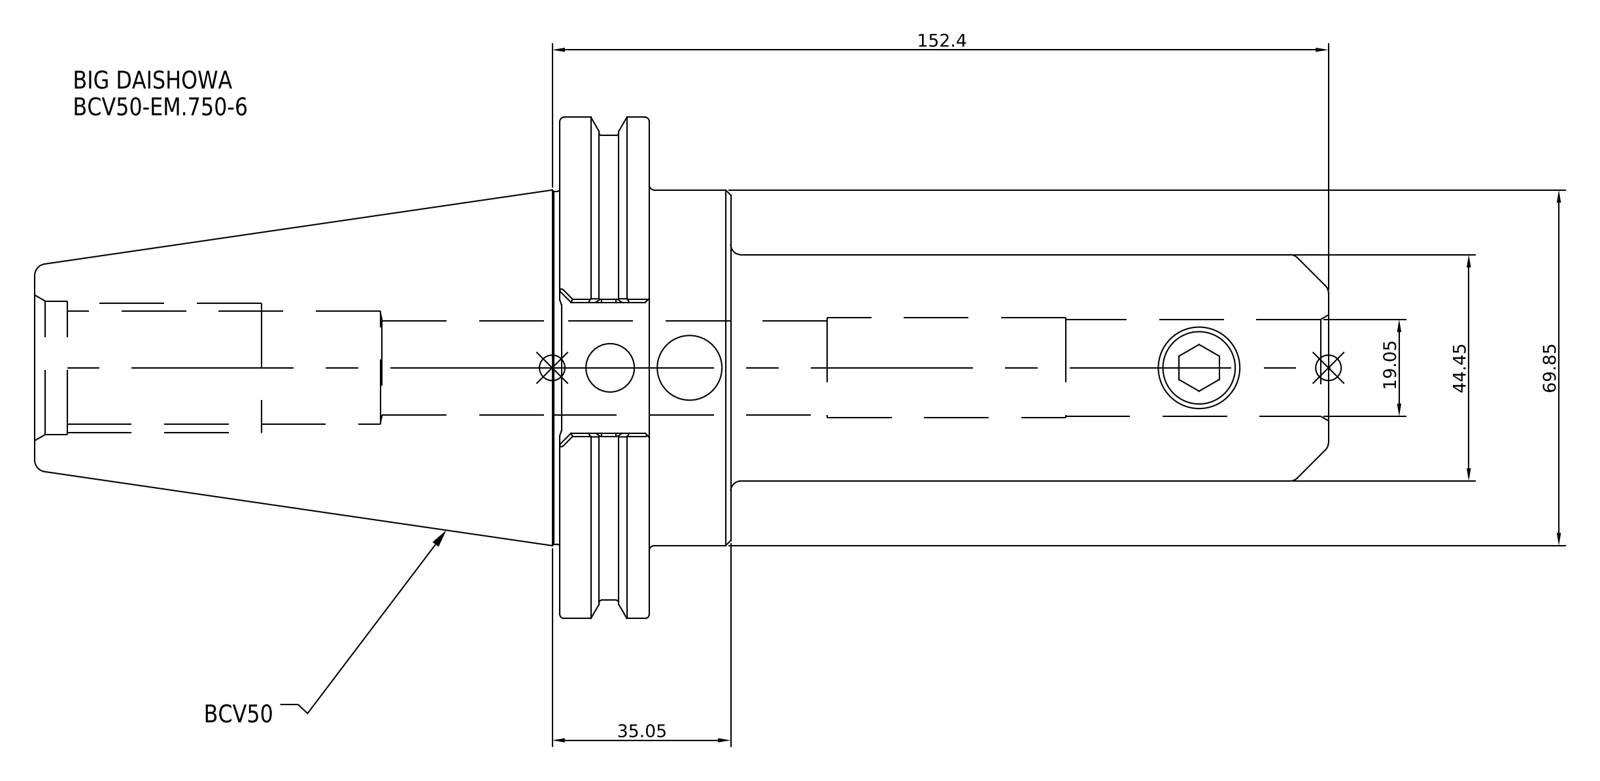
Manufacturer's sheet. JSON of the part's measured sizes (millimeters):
{"part_name": "BCV50-EM_750-6", "step_written_by": "SolidWorks 2021 (CONFIG_CONTROL_DESIGN)", "units": "millimeters", "bodies": {"solids": 1, "faces": 30, "planar": 8, "cylindrical": 14, "other": 8}, "overall_size": [254, 98.43, 98.43], "volume_mm3": 588332, "surface_area_mm2": 63806, "round_holes": [[19.1, 1]], "round_bosses_or_shafts": [[98.43, 1], [91.29, 1], [69.85, 1], [44.45, 1]], "face_to_face_distances": [17.55, 16, 33.55, 136.65, 120.65, 103.1, 117.35, 133.35, 150.9, 254]}
